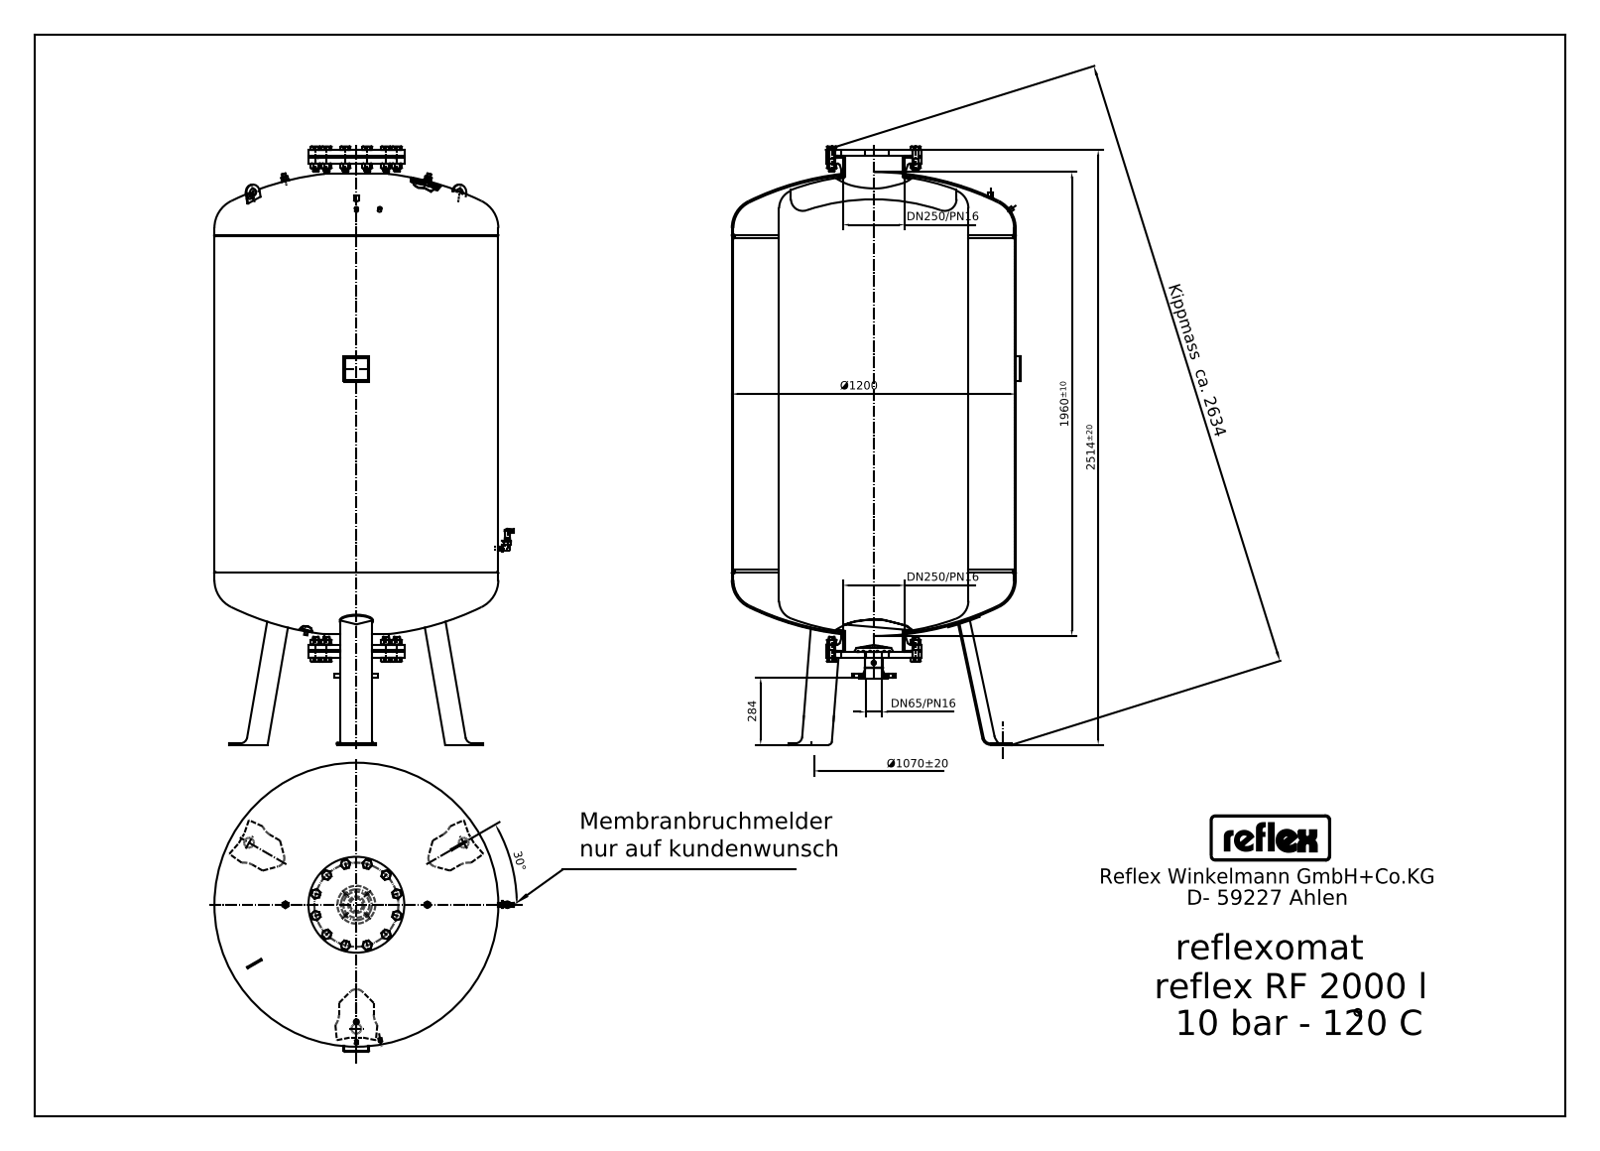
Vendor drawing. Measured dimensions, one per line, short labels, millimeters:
written by: Mechanical Desktop 2009 (CONFIG_CONTROL_DESIGN)
unit: mm
bodies: 23 solids, 940 faces (556 planar, 222 cylindrical, 162 other)
size: 2510 × 1266 × 1220
volume: 2 045 000 000 mm³; area: 15 080 000 mm²
holes: 2× ⌀11.45, 1× ⌀3.5, 1× ⌀14.95, 1× ⌀30, 1× ⌀260.4
bosses: 12× ⌀16, 3× ⌀21.3, 3× ⌀18.5, 2× ⌀28, 2× ⌀20, 1× ⌀1200, 1× ⌀375, 1× ⌀273
rounds: 18× R25, 5× R1, 4× R8.44, 3× R3.38, 3× R6, 3× R9, 2× R2, 2× R3
face distances: 1450, 22, 2116, 27, 2089, 1763, 313, 1785, 335, 353
hole spacings: 495, 619.5, 792.97
